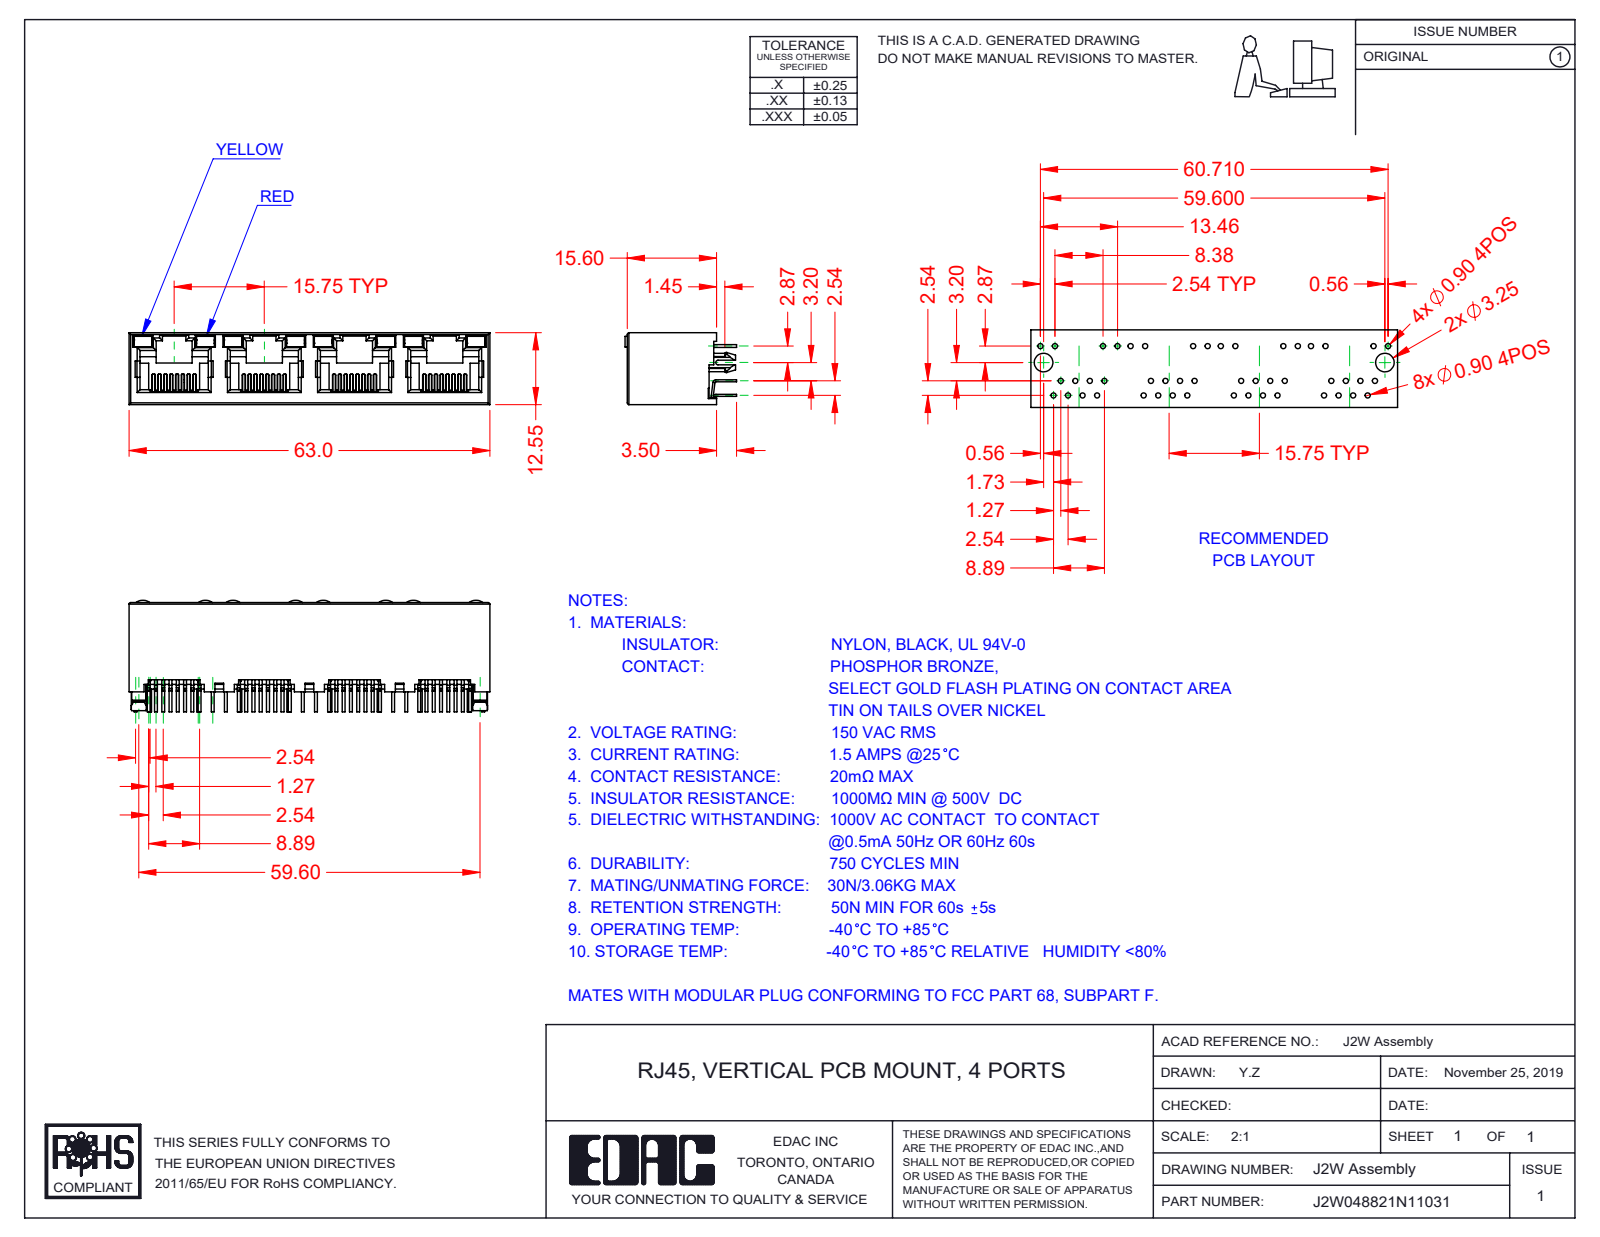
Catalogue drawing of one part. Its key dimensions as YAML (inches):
part_name: "2W LED LH_1-Yellow; 2W Insulator; J2W048821N12131; 2W Contact Lock (+2 more)"
step_written_by: "SolidWorks 2016 (CONFIG_CONTROL_DESIGN)"
units: inches
bodies: {solids: 45, faces: 3135, planar: 2600, cylindrical: 477, other: 58}
overall_size: [2.48, 0.768, 0.494]
volume: 0.326
surface_area: 20.37
partial_cylinders:
  - {radius: 0.006, count: 64}
  - {radius: 0.008, count: 29}
  - {radius: 0.02, count: 28}
  - {radius: 0.012, count: 14}
  - {radius: 0.018, count: 8}
  - {radius: 0.079, count: 8}
  - {radius: 0.01, count: 2}
  - {radius: 0.059, count: 2}
face_to_face_distances: [0.494, 0.469, 0.026, 0.62, 0.014, 0.059, 0.031, 0.024, 0.445, 1.24]
